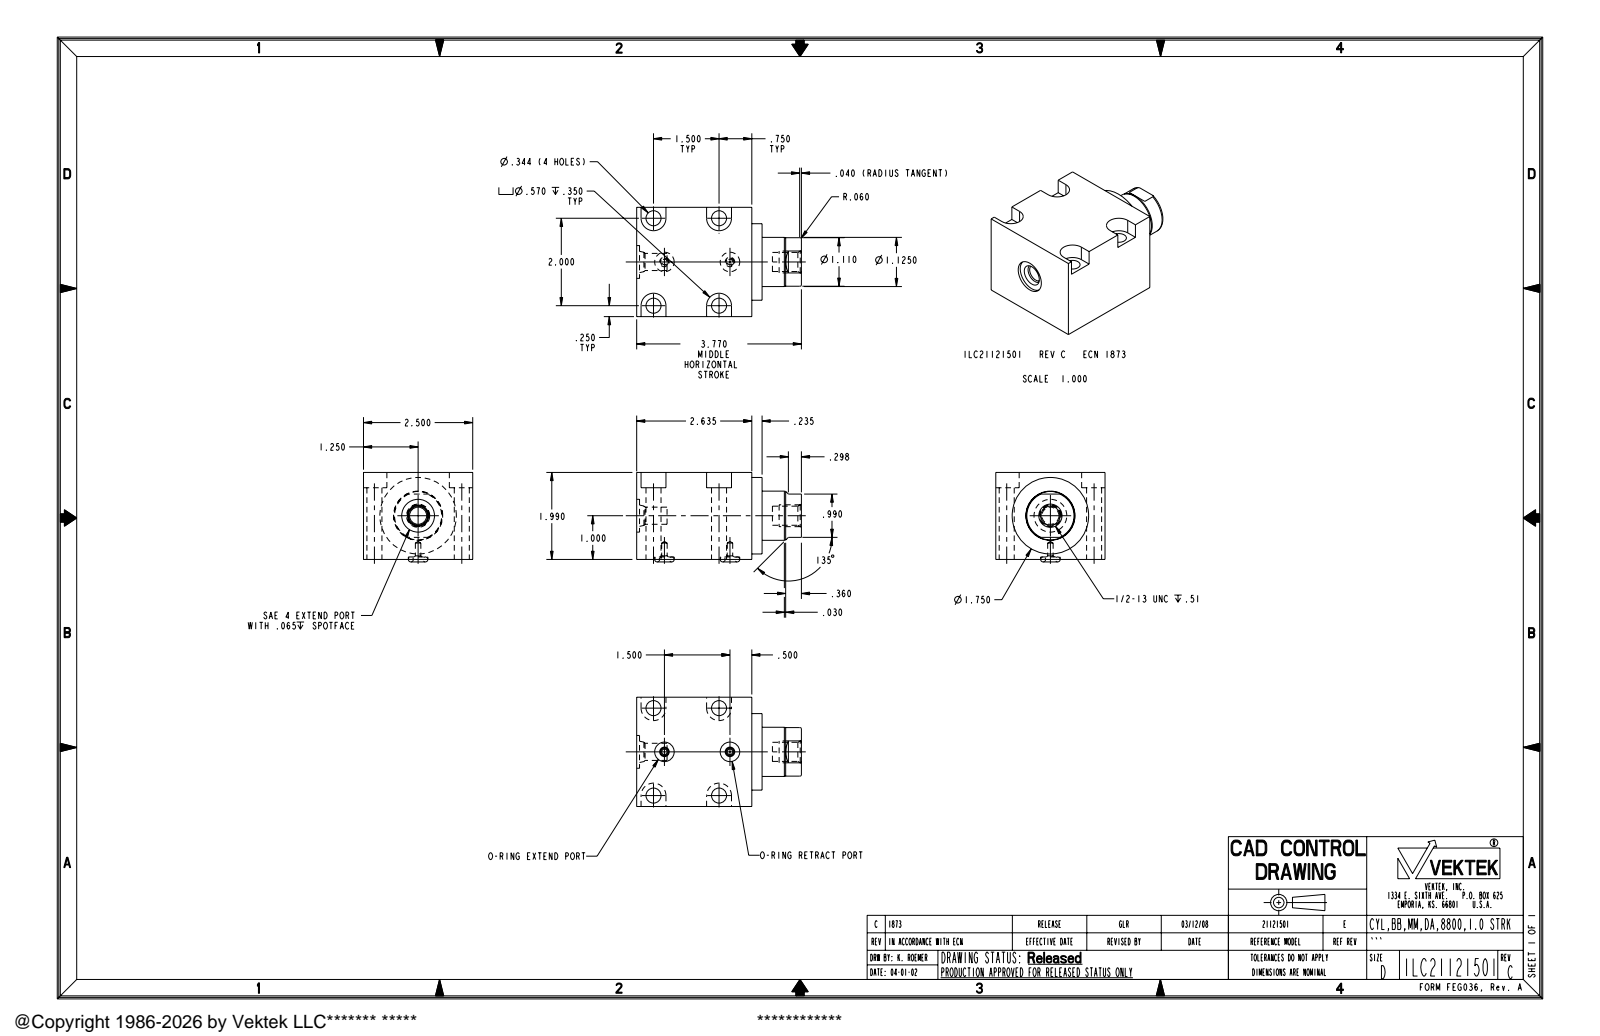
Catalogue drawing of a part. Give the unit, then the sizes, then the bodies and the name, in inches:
Units: inches
Overall size (bounding box): 3.77 × 2.5 × 2.047
Round holes (diameter × count): ⌀0.344 ×4, ⌀0.125 ×2, ⌀0.447 ×2, ⌀0.392 ×1, ⌀0.437 ×1, ⌀0.75 ×1
Round bosses / shafts (diameter × count): ⌀1.75 ×1, ⌀1.125 ×1, ⌀1.11 ×1, ⌀0.5 ×1
Partial cylindrical surfaces — rounded edges, fillets, slot ends (radius × count): R0.285 ×4
Main face-to-face distances: 1.99, 2.5, 2.635, 0.235, 2.87, 1.135, 1.64, 0.35, 0.9, 3.77
Hole centre spacings: 1.031, 1.5, 1.601, 2, 2.016, 2.5
Volume: 13.34 in³ · Surface area: 49.21 in²
Bodies: 1 solid, 90 faces (30 planar, 34 cylindrical, 26 other)
Part name (STEP PRODUCT): ILC21121501
STEP written by: PRO/ENGINEER BY PARAMETRIC TECHNOLOGY CORPORATION, 2007460 (AUTOMOTIVE_DESIGN_CC2)
